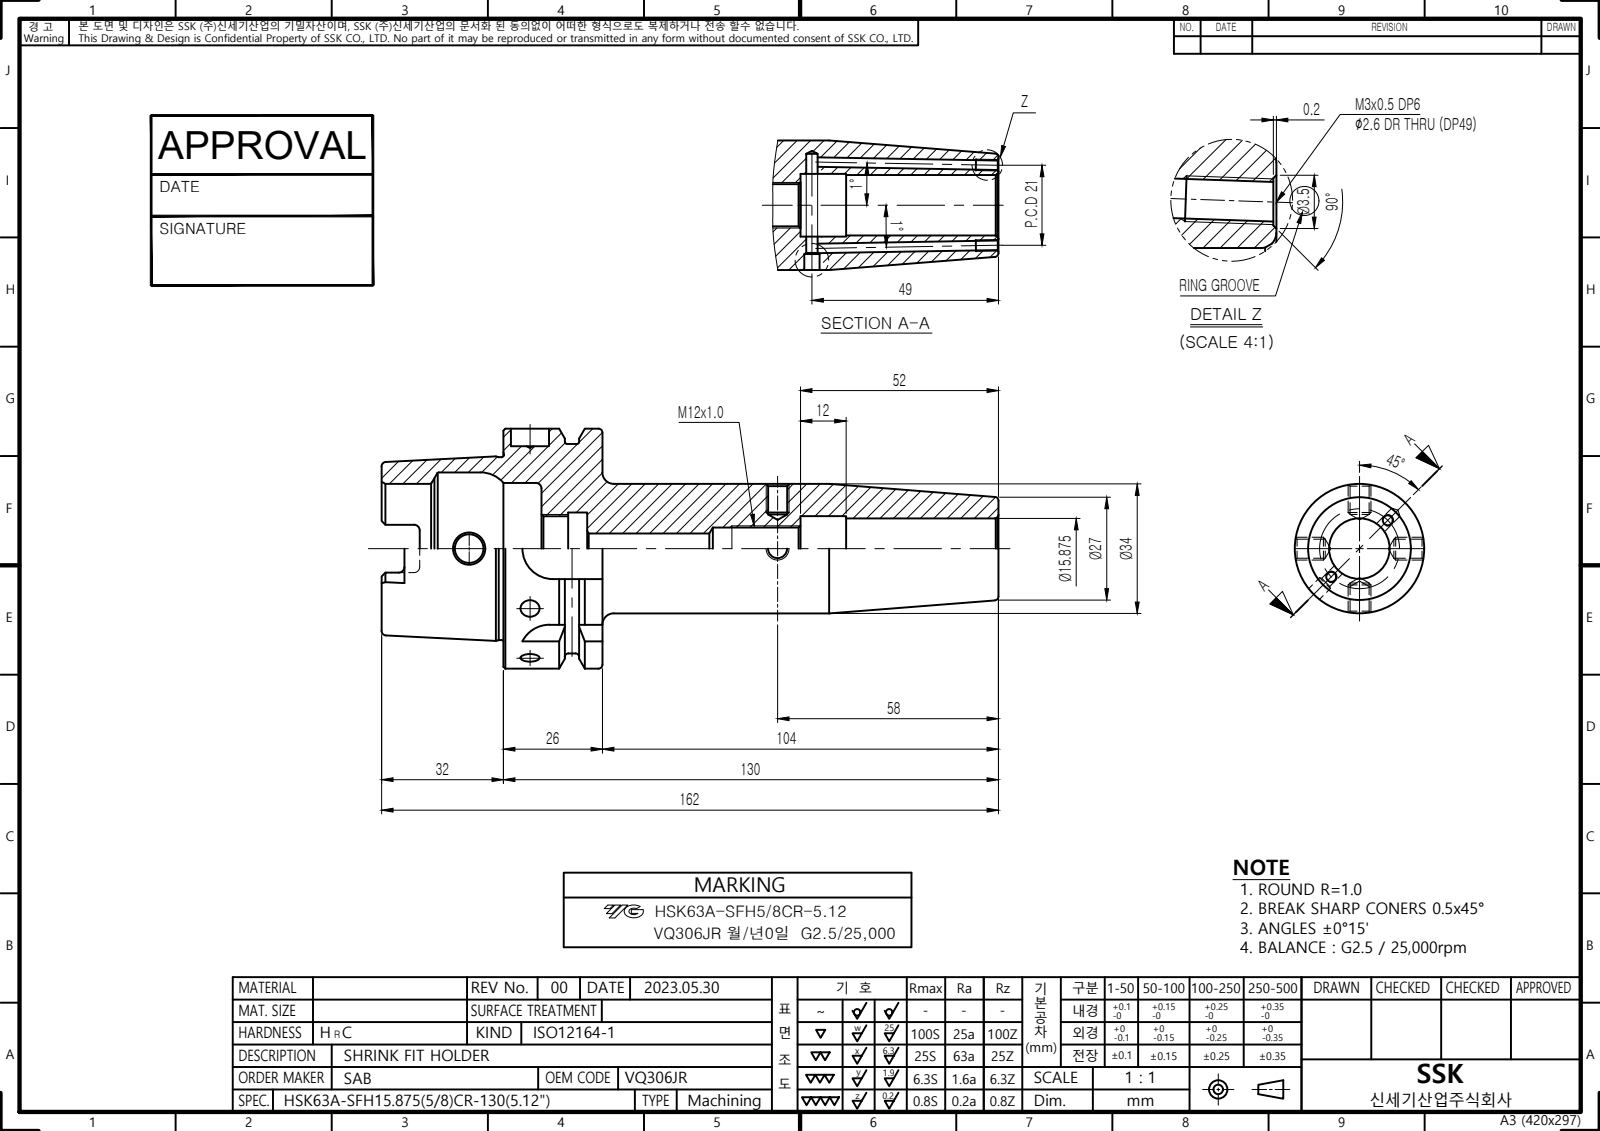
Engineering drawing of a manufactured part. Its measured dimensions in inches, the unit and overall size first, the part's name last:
Units: inches
Overall size (bounding box): 6.378 × 2.48 × 2.48
Round holes (diameter × count): ⌀0.097 ×2, ⌀0.295 ×1, ⌀0.331 ×1, ⌀0.394 ×1, ⌀0.43 ×1, ⌀0.625 ×1, ⌀0.666 ×1, ⌀0.669 ×1, ⌀0.748 ×1, ⌀1.339 ×1, ⌀1.575 ×1
Round bosses / shafts (diameter × count): ⌀2.48 ×1, ⌀2.165 ×1, ⌀1.891 ×1
Partial cylindrical surfaces — rounded edges, fillets, slot ends (radius × count): R0.059 ×6, R0.113 ×4, R0.315 ×4
Main face-to-face distances: 1.024, 0.394, 0.63, 1.26, 1.654, 2.283, 2.047, 2.087, 4.094, 0.866
Volume: 9.379 in³ · Surface area: 57.86 in²
Bodies: 1 solid, 121 faces (42 planar, 36 cylindrical, 43 other)
Part name (STEP PRODUCT): LO-HSK63A-SFH15.875CR-130
STEP written by: Autodesk Inventor 2022 (AUTOMOTIVE_DESIGN)
